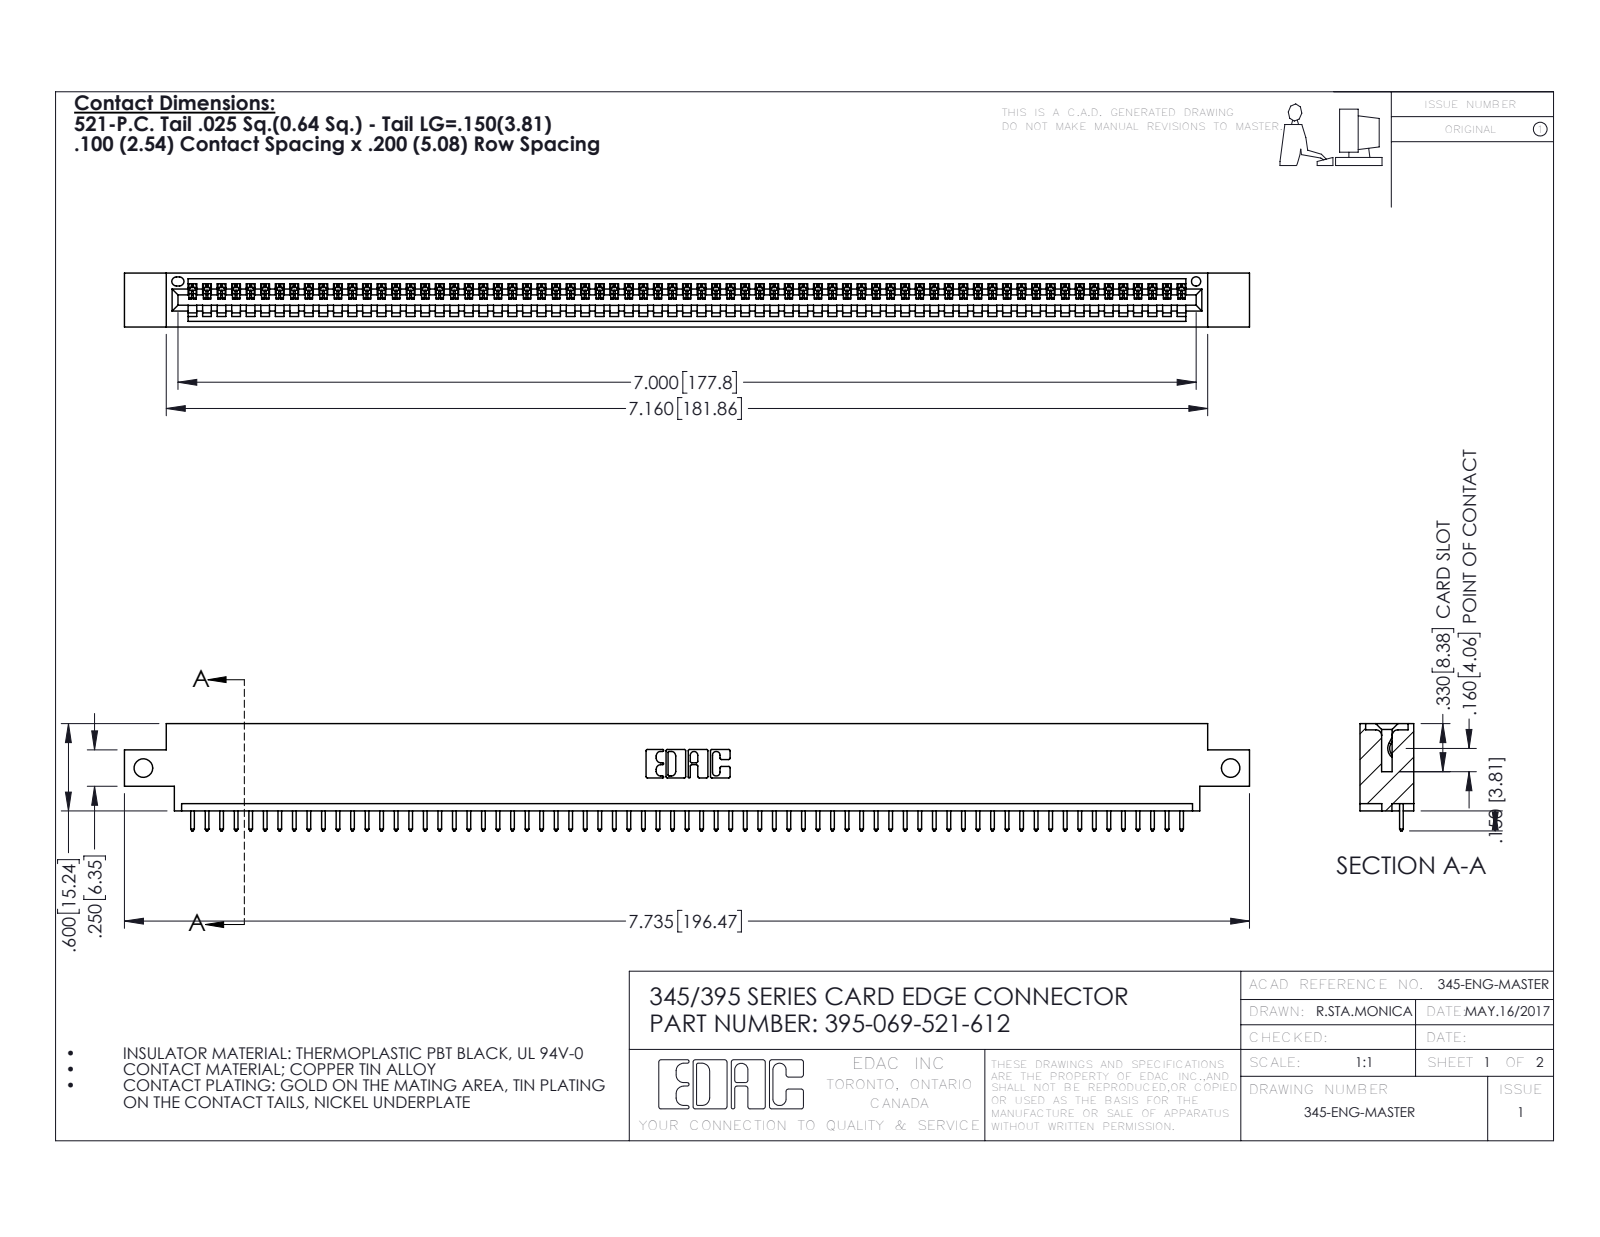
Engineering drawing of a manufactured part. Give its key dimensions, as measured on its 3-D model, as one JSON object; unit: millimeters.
{"part_name": "395-069-521-612; 345-292-001_345-293-121; 345 Part_0.170 Offset - Side Mount", "step_written_by": "SolidWorks 2016 (CONFIG_CONTROL_DESIGN)", "units": "millimeters", "bodies": {"solids": 70, "faces": 4132, "planar": 2844, "cylindrical": 1288, "other": 0}, "overall_size": [196.5, 18.7, 9.4], "volume_mm3": 18480, "surface_area_mm2": 24150, "round_holes": [[3.3, 2], [1.6, 1]], "partial_cylinders_radius": [[0.2, 138], [0.3, 138], [0.3, 22], [0.2, 6], [0.8, 6], [0.7, 3], [0.8, 2], [1, 2]], "face_to_face_distances": [7.6, 1.8, 9.4, 5.1, 2.5, 6.9, 0.6, 5.7, 4.4, 3.8], "hole_center_spacings": [189.9]}
